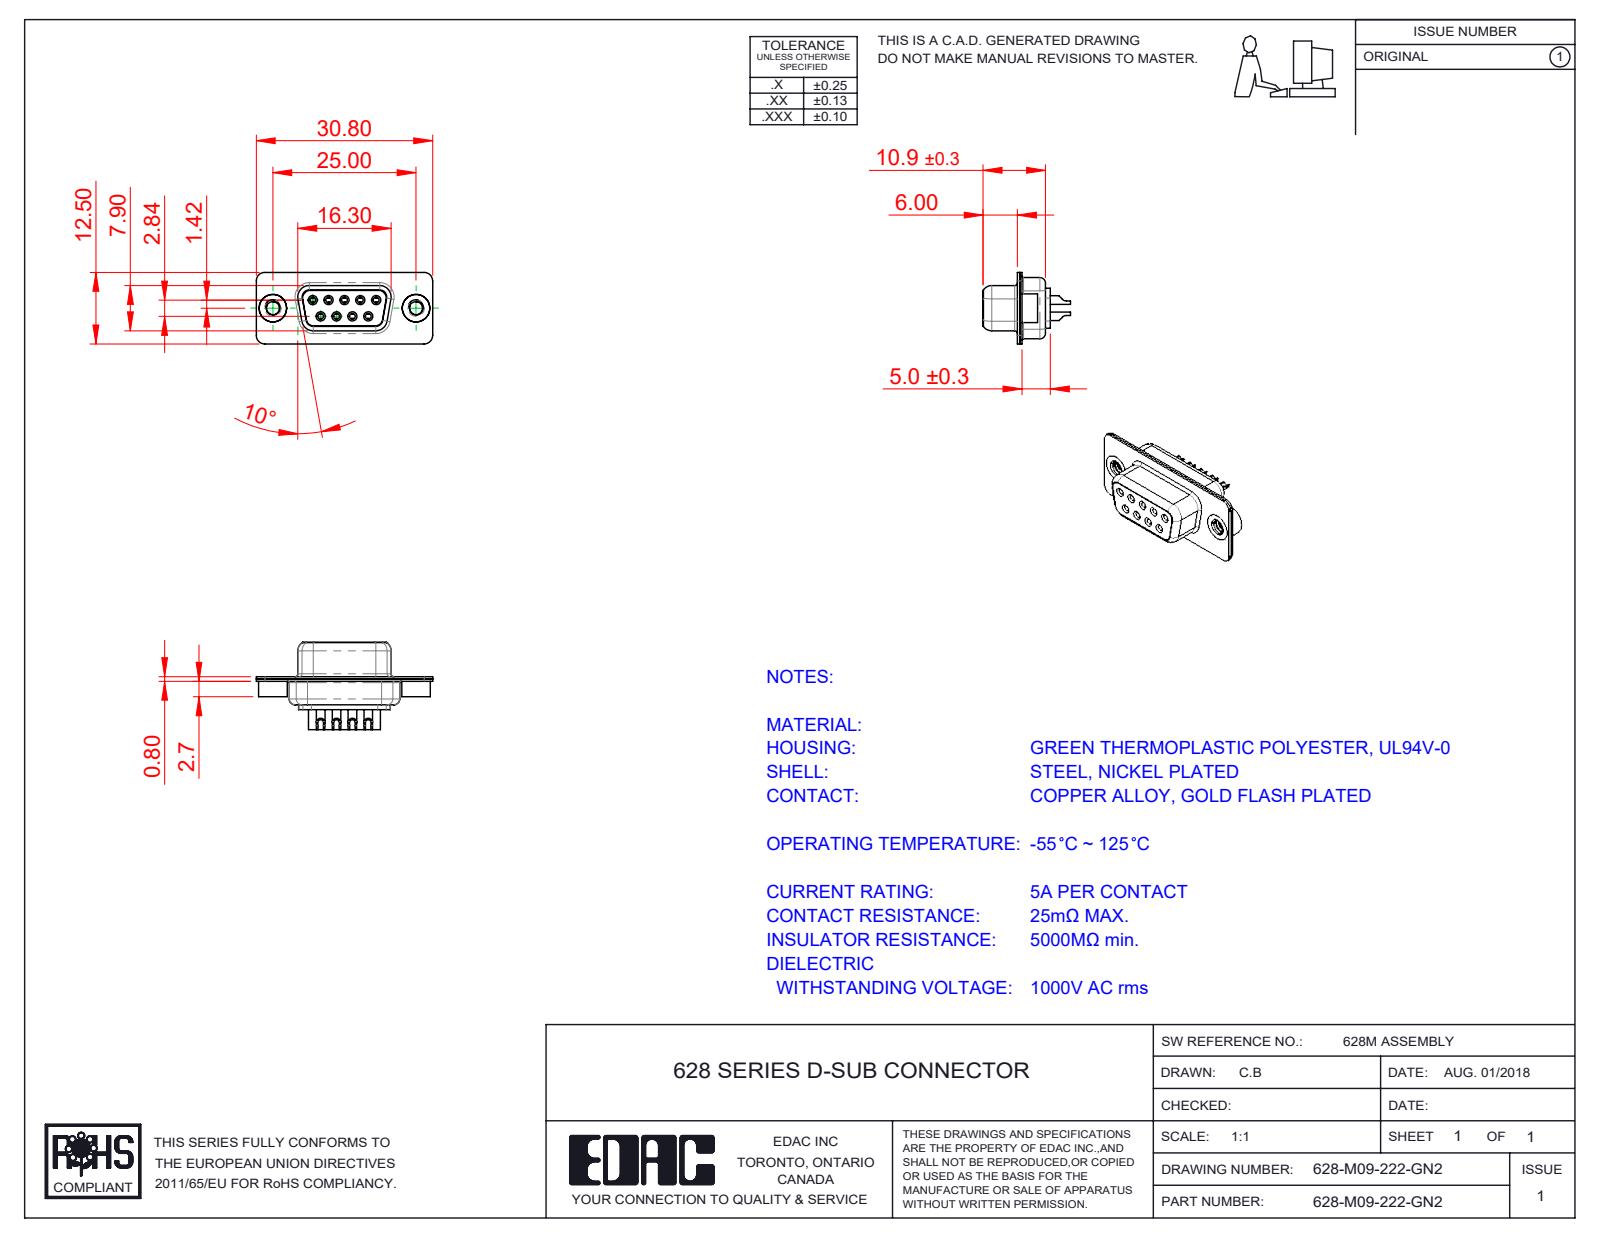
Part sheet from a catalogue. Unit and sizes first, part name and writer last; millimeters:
Units: millimetres
Overall size (bounding box): 30.8 × 15.25 × 12.5
Round holes (diameter × count): ⌀1 ×9, ⌀1.1 ×9, ⌀1.7 ×9, ⌀1.8 ×9, ⌀2 ×9, ⌀2.26 ×2, ⌀4 ×2, ⌀4.8 ×2
Round bosses / shafts (diameter × count): ⌀2.2 ×9, ⌀1.6 ×9, ⌀1.5 ×9, ⌀5 ×2, ⌀4.9 ×2
Partial cylindrical surfaces — rounded edges, fillets, slot ends (radius × count): R1.5 ×16, R2 ×12, R1.35 ×8, R1.6 ×8, R1 ×6, R0.25 ×4, R0.5 ×4, R0.6 ×4
Main face-to-face distances: 0.4, 1.4, 0.45, 8.45, 0.8, 8.9, 1.8, 1, 7.05, 0.85
Hole centre spacings: 3.16, 2.77, 5.54, 5.03, 5.04, 8.31, 7.1, 7.48
Volume: 1 717 mm³ · Surface area: 4 505 mm²
Bodies: 14 solids, 775 faces (221 planar, 326 cylindrical, 228 other)
Part name (STEP PRODUCT): 628-M09-222-GN2; 628M Housing_09 Contacts; 628M Shell Front_09 Contacts; 628M Shell Rear_09 Contacts (+3 more)
STEP written by: SolidWorks 2020 (CONFIG_CONTROL_DESIGN)
